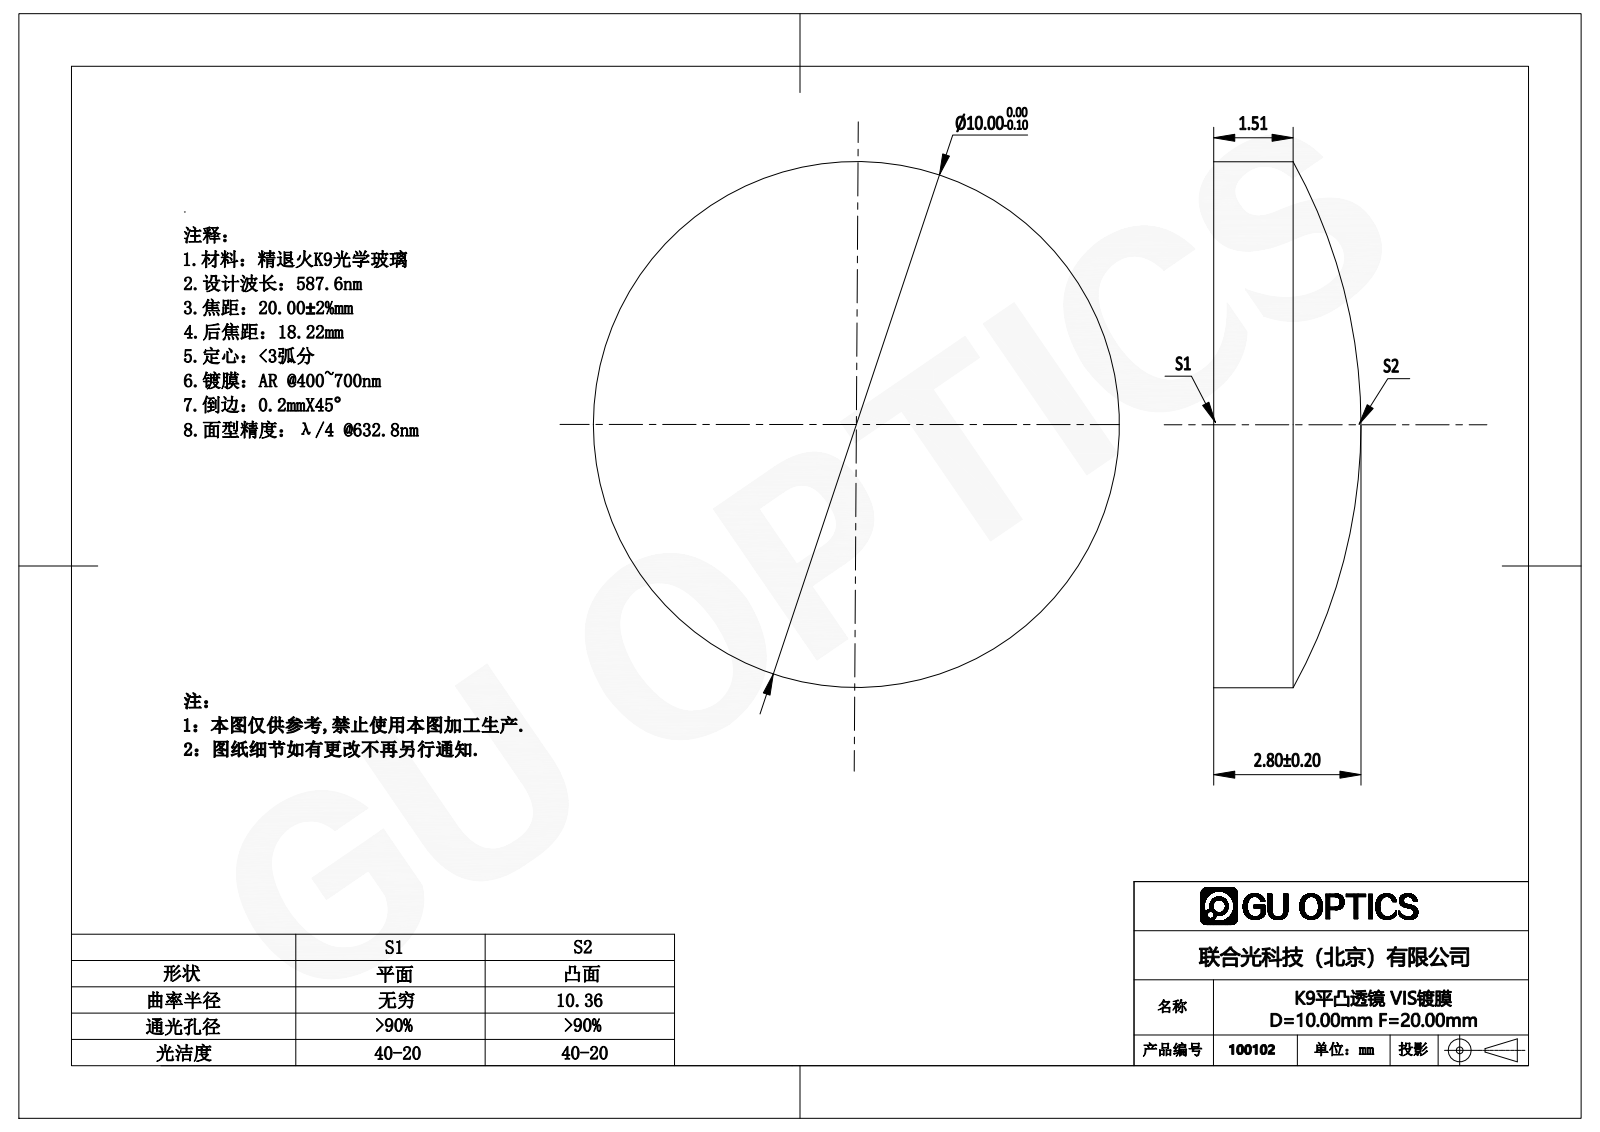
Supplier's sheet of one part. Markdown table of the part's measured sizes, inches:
| quantity | value |
| --- | --- |
| part name | 100102 |
| STEP written by | SolidWorks 2016 (AUTOMOTIVE_DESIGN) |
| units | inches |
| bodies | 1 solid, 5 faces (1 planar, 2 cylindrical, 2 other) |
| overall size | 0.394 × 0.394 × 0.11 |
| volume | 0.01 in³ |
| surface area | 0.326 in² |
| round bosses / shafts (diameter × count) | 0.394 × 1 |
